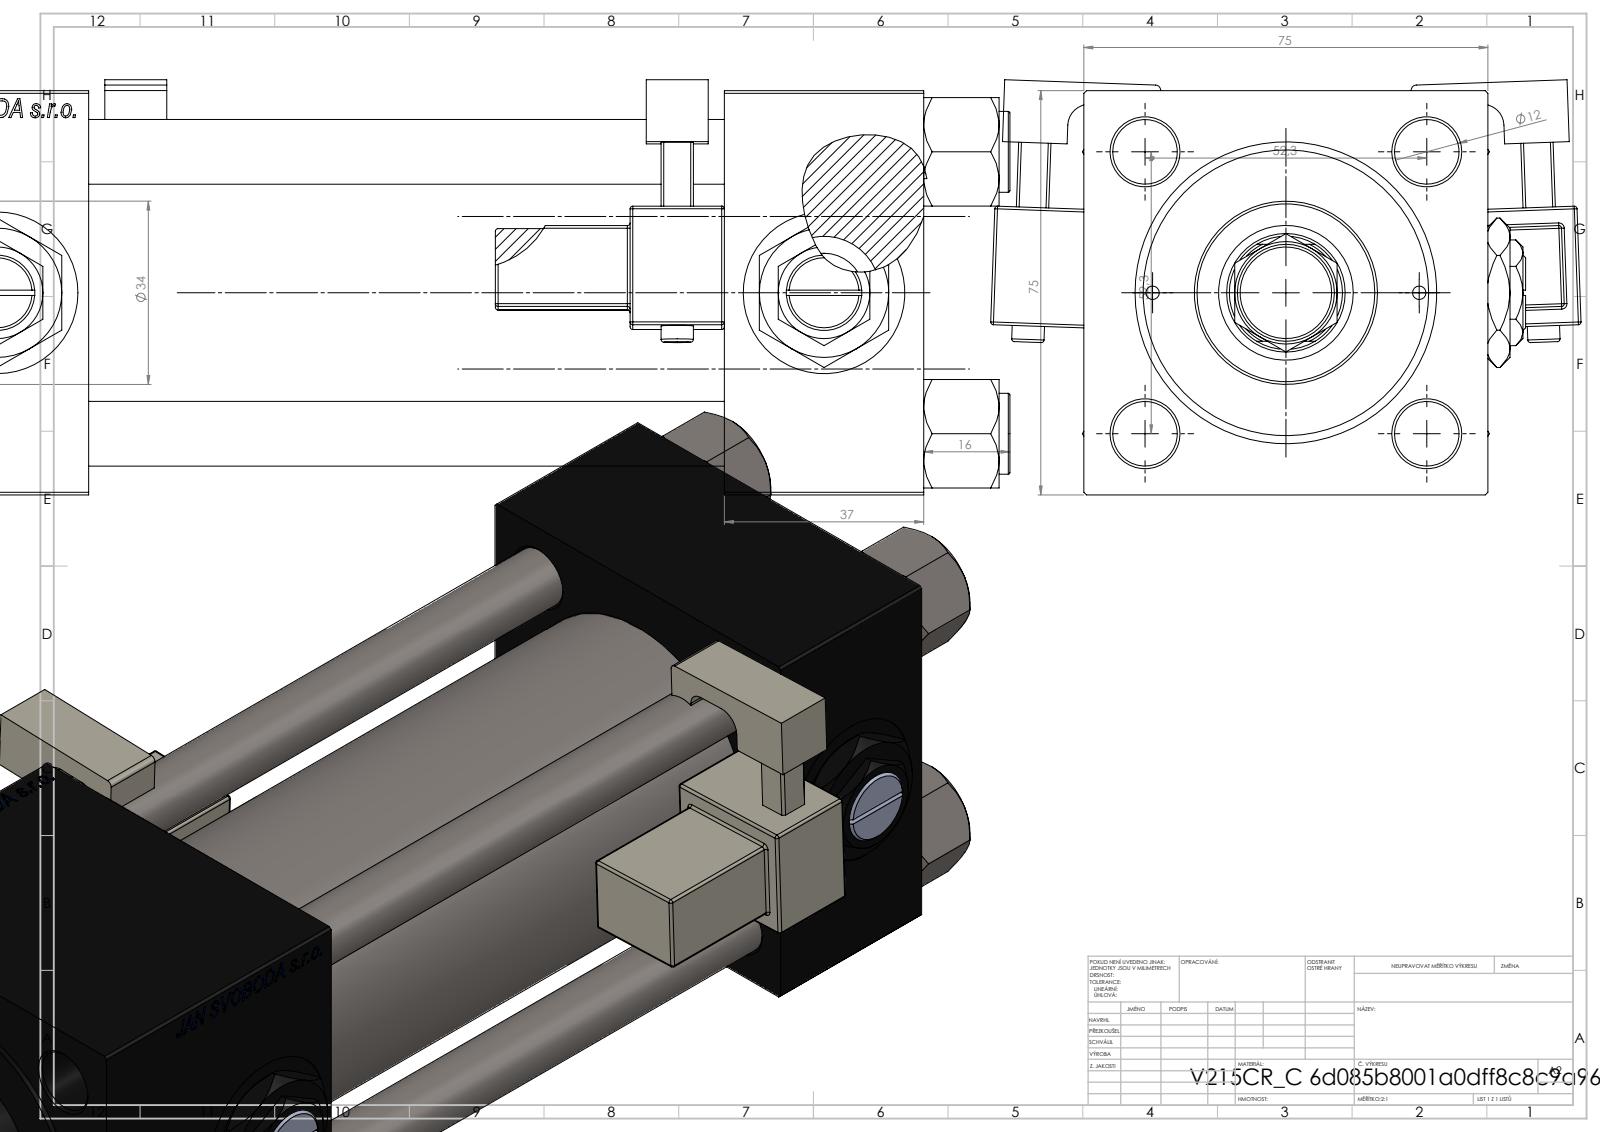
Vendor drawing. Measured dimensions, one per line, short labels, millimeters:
name: NUT_M5_C; V215CR_MSU; V215CR_VCP_C; MFA (+4 more)
written by: SolidWorks 2019 (CONFIG_CONTROL_DESIGN)
unit: mm
bodies: 16 solids, 1461 faces (649 planar, 166 cylindrical, 646 other)
size: 288 × 109.57 × 77.03
volume: 780 925 mm³; area: 199 983 mm²
holes: 4× ⌀12, 2× ⌀2.5, 2× ⌀7, 2× ⌀20.96, 2× ⌀30, 1× ⌀10.5, 1× ⌀22, 1× ⌀25, 1× ⌀41, 1× ⌀50, 1× ⌀53
bosses: 4× ⌀15, 2× ⌀6, 1× ⌀56, 1× ⌀34, 1× ⌀18, 1× ⌀11
rounds: 48× R0.5, 2× R1, 2× R2.5, 2× R4, 1× R10.5
face distances: 75, 37, 214, 177, 155, 118, 59, 185.3, 148.3, 30.3
hole spacings: 26.19, 36.98, 52.3, 57.22, 24.75, 73.96, 49.5, 153.5
